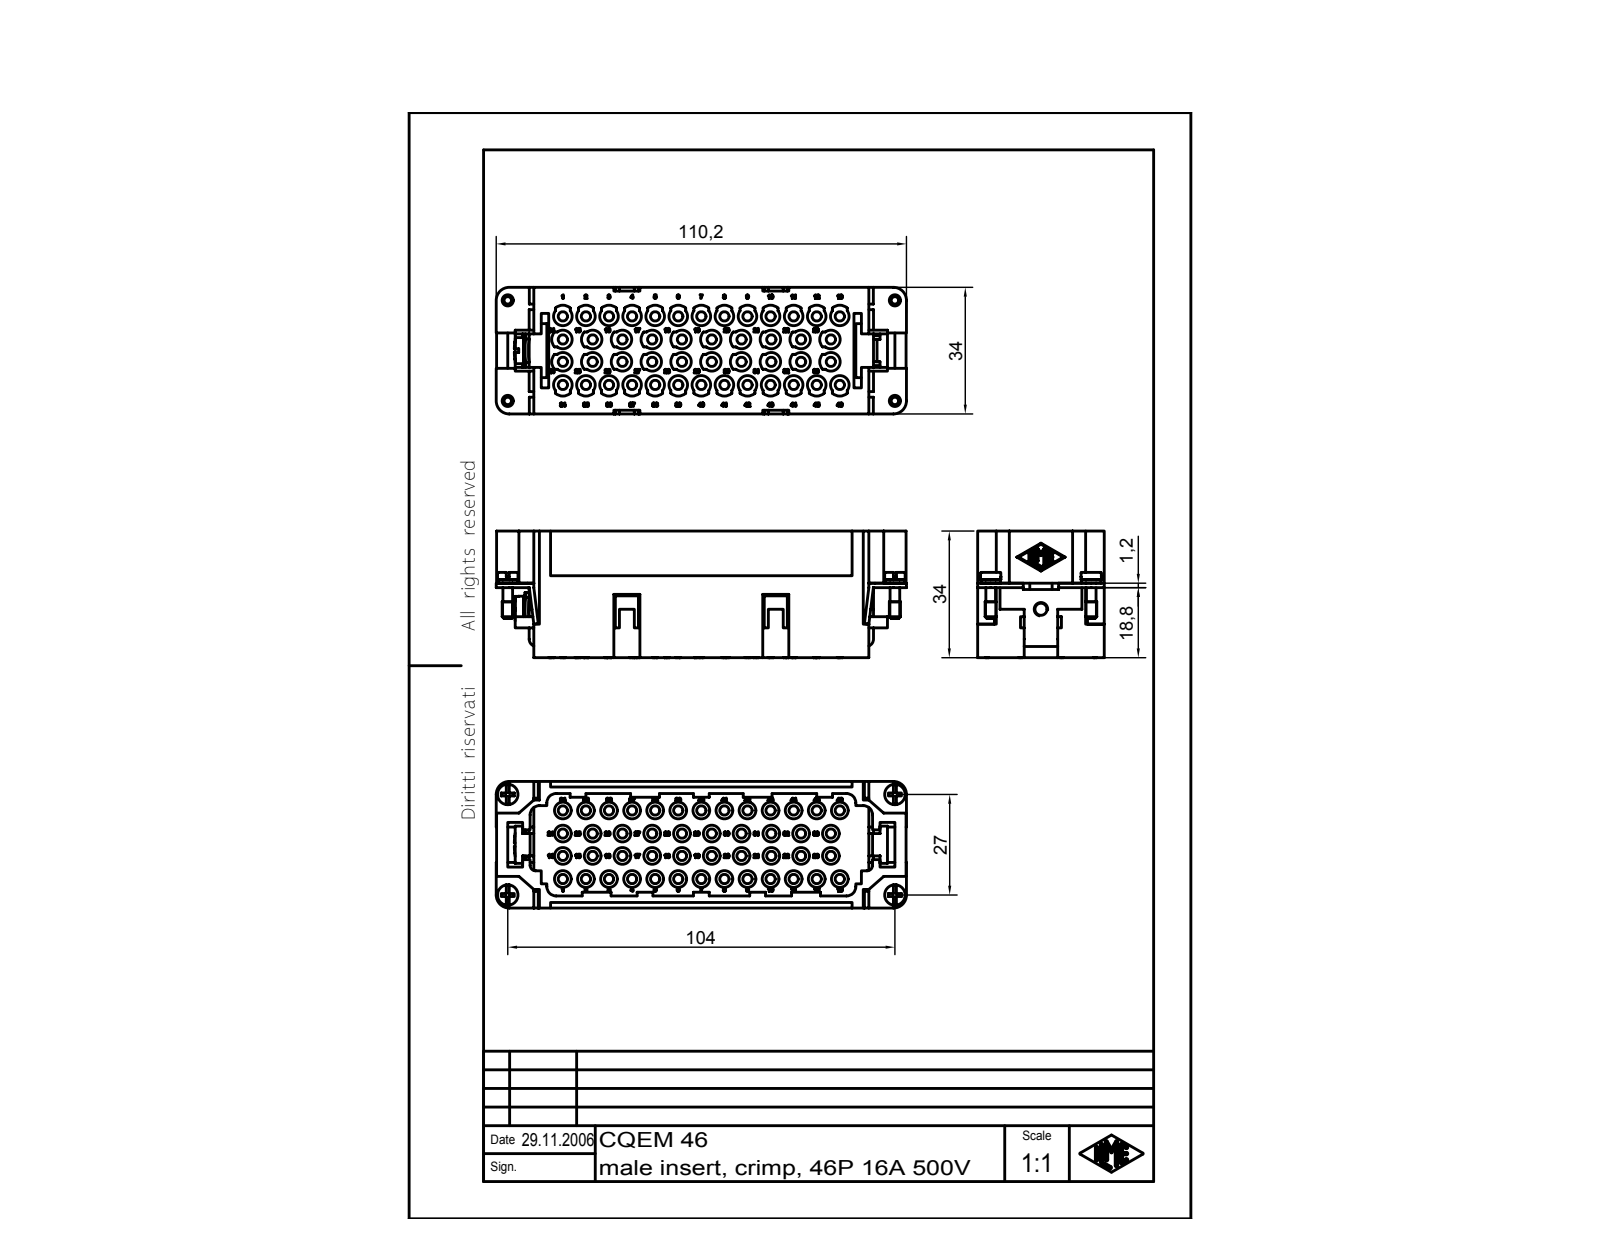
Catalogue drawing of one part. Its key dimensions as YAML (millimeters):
part_name: "CQEM 46"
step_written_by: "Autodesk Inventor 7 (AUTOMOTIVE_DESIGN)"
units: millimeters
bodies: {solids: 1, faces: 3433, planar: 1497, cylindrical: 347, other: 1589}
overall_size: [110.2, 34.01, 34]
volume: 53884
surface_area: 42089
round_holes:
  - {diameter: 2.5, count: 46}
  - {diameter: 3.24, count: 1}
round_bosses_or_shafts:
  - {diameter: 4.5, count: 46}
  - {diameter: 5.5, count: 2}
  - {diameter: 5.3, count: 2}
  - {diameter: 3, count: 2}
  - {diameter: 2.6, count: 2}
  - {diameter: 7, count: 1}
partial_cylinders:
  - {radius: 2.5, count: 39}
  - {radius: 3, count: 33}
  - {radius: 0.25, count: 14}
  - {radius: 2, count: 4}
  - {radius: 1.5, count: 2}
  - {radius: 3.5, count: 2}
  - {radius: 5.5, count: 1}
face_to_face_distances: [34, 20, 3.25, 1, 1.5, 30.75, 4.25, 4, 14.5, 7]
hole_center_spacings: [6.2, 19.42, 12.4, 22.19, 18.6, 26.16, 24.8, 30.88]
